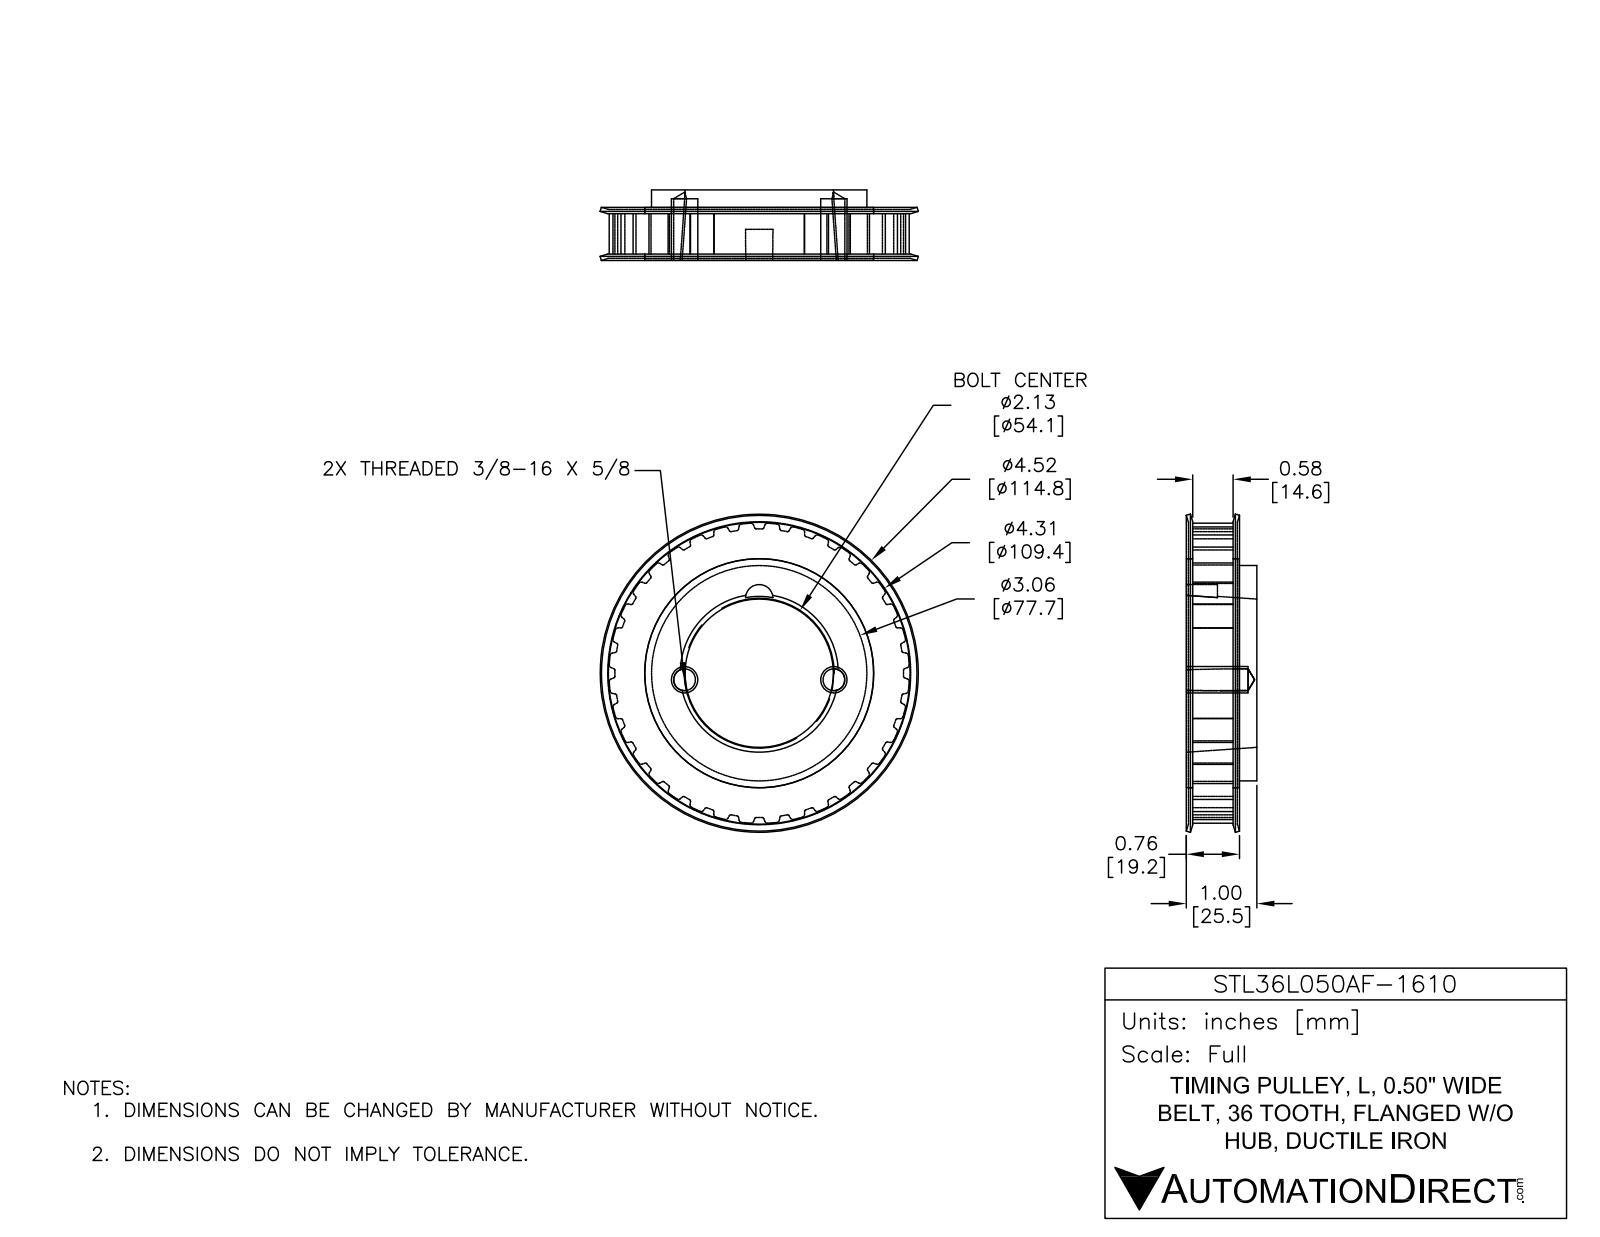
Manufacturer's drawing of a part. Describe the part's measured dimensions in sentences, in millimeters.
The part is named "STL36L050AF-1610". Its 3-D file was written by "SolidWorks 2018 (AUTOMOTIVE_DESIGN)". It is 4 solids with 359 faces: 118 planar, 223 cylindrical and 18 other. Overall it measures 114.77 by 114.77 by 25.46 millimeters. Its volume is 140 029 cubic millimeters and its surface area 50 691 square millimeters. Round holes: 1 of diameter 94.7. Round bosses or shafts: 1 of diameter 77.72. Partial cylindrical surfaces (rounded edges, fillets, slot ends): 72 of radius 0.38, 72 of radius 0.51, 2 of radius 3.94, 1 of radius 4.95, 1 of radius 54.2. The main face-to-face distances are 2.22, 16.83, 0.7, 18.35, 1.52, 16.13, 14.61, 8.57, 23.18, 25.4.
